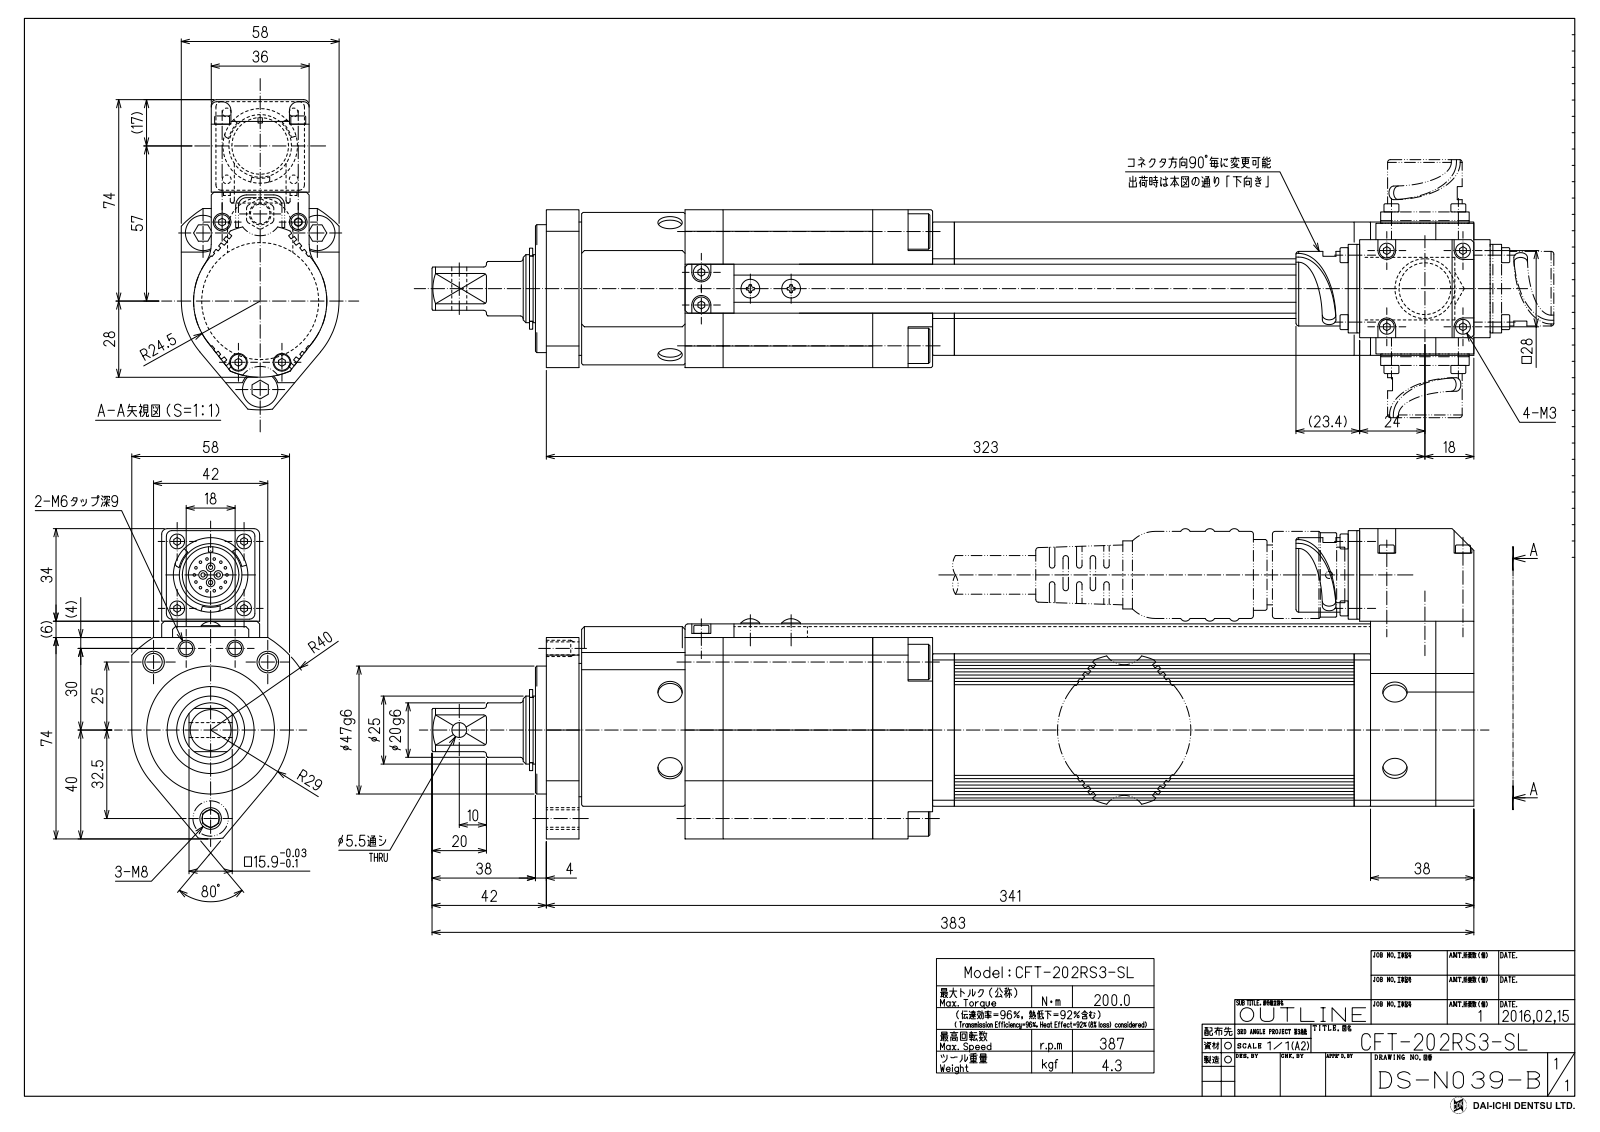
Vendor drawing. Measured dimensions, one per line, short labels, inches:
name: CFT-202RS3-SL_TOP; CFT-202RS3-SL
written by: SolidWorks 2014 (CONFIG_CONTROL_DESIGN)
unit: in
bodies: 15 solids, 416 faces (156 planar, 176 cylindrical, 84 other)
size: 15.079 × 4.488 × 2.283
volume: 58.86 in³; area: 232.3 in²
holes: 3× ⌀0.268, 2× ⌀0.197, 1× ⌀0.217, 1× ⌀0.819, 1× ⌀0.866
bosses: 8× ⌀0.217, 3× ⌀0.512, 2× ⌀0.26, 2× ⌀0.232, 1× ⌀2.205, 1× ⌀1.929, 1× ⌀1.85, 1× ⌀1.079
rounds: 42× R0.039, 6× R0.079, 4× R0.128, 4× R0.315, 3× R0.276, 2× R0.118, 2× R0.138, 2× R0.472
face distances: 0.039, 1.496, 0.551, 2.165, 10.866, 2.717, 0.394, 0.433, 0.866, 0.157
hole spacings: 0.512, 1.12, 1.197, 1.507, 2.41, 2.486, 0.709, 1.654
